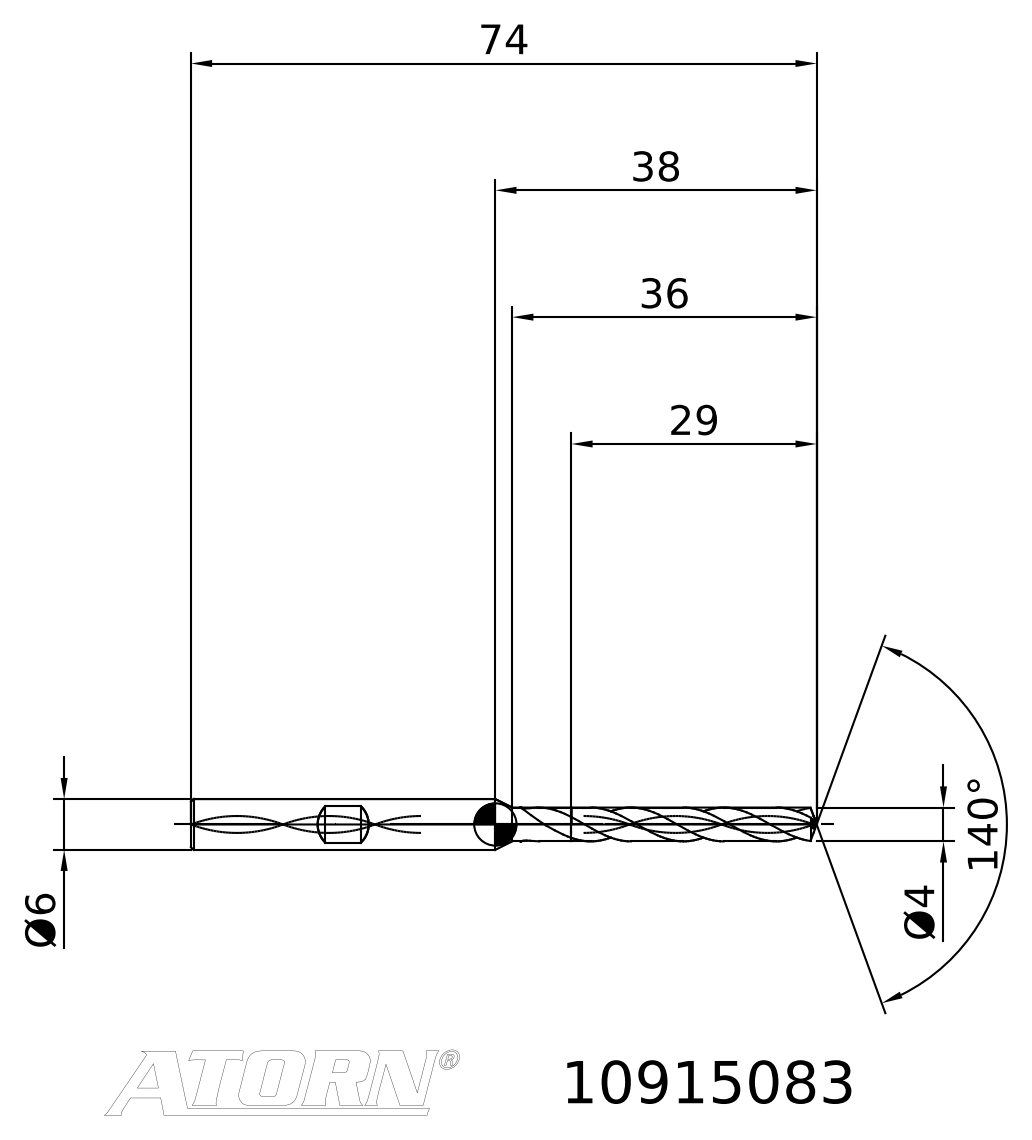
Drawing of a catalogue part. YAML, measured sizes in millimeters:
step_written_by: "TDM (AUTOMOTIVE_DESIGN)"
units: millimeters
bodies: {solids: 2, faces: 35, planar: 8, cylindrical: 0, other: 27}
overall_size: [74, 6, 6]
volume: 1345
surface_area: 1250
face_to_face_distances: [45, 28.45, 73.45]
